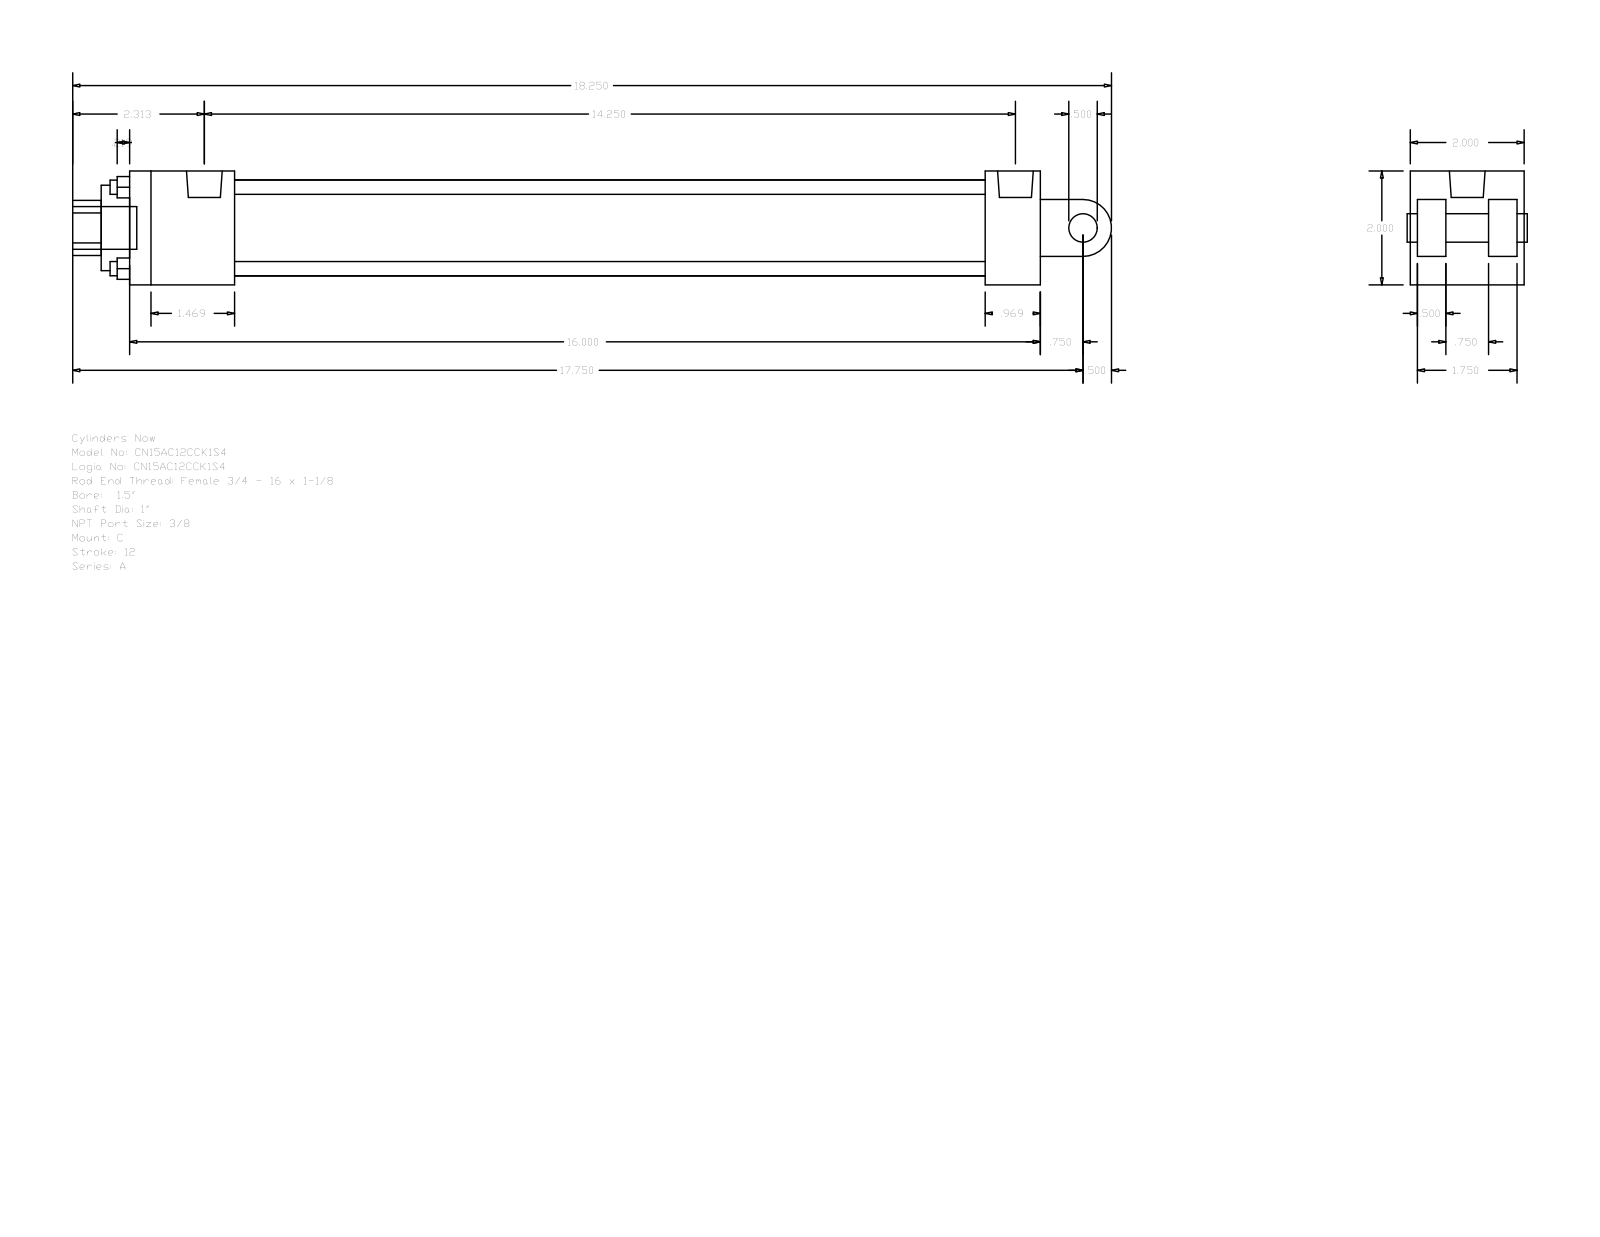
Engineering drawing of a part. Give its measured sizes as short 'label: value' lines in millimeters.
name: A_C__0150_1
written by: GSSL Pune (CONFIG_CONTROL_DESIGN)
unit: mm
bodies: 0 solids, 99 faces (70 planar, 29 cylindrical, 0 other)
size: 463.55 × 50.8 × 50.8
holes: 4× ⌀6.35, 2× ⌀5.56, 1× ⌀15.93, 1× ⌀25.4, 1× ⌀38.1, 1× ⌀42.93
bosses: 2× ⌀5.56, 1× ⌀19.05, 1× ⌀15.93, 1× ⌀12.7
rounds: 1× R12.29, 1× R12.7
face distances: 50.8, 12.7, 3.17, 15.87, 34.93, 47.63, 31.76, 406.4, 381.79, 24.61
hole spacings: 25.68, 36.32, 51.36, 3.97
